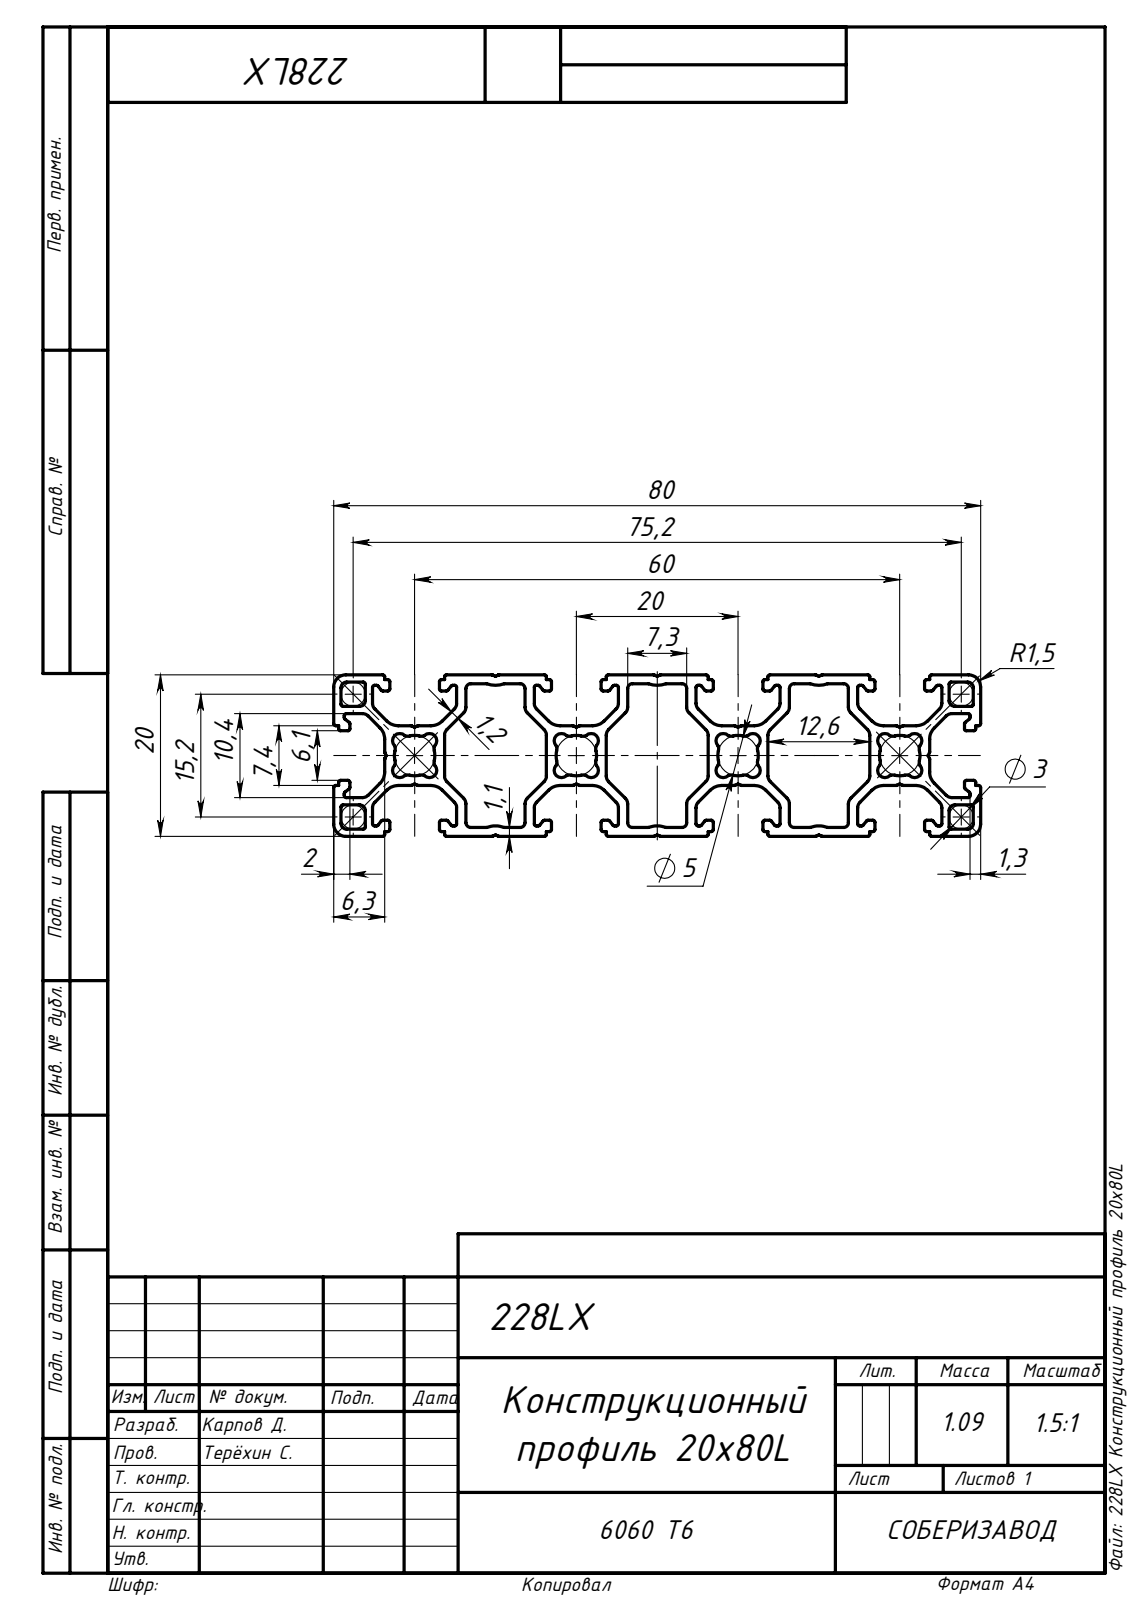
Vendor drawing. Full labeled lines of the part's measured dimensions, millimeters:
STEP written by: SolidWorks 2019 (AUTOMOTIVE_DESIGN)
Units: millimetres
Bodies: 1 solid, 610 faces (292 planar, 318 cylindrical, 0 other)
Overall size (bounding box): 1000 × 80 × 20
Volume: 402 052 mm³ · Surface area: 681 212 mm²
Partial cylindrical surfaces — rounded edges, fillets, slot ends (radius × count): R0.25 ×160, R1 ×76, R2 ×20, R0.9 ×16, R0.6 ×12, R0.7 ×8, R3 ×6, R1.5 ×4
Main face-to-face distances: 20, 14.14, 1.1, 12.6, 13.7, 1.15, 0.9, 14.19, 28.28, 2.65
